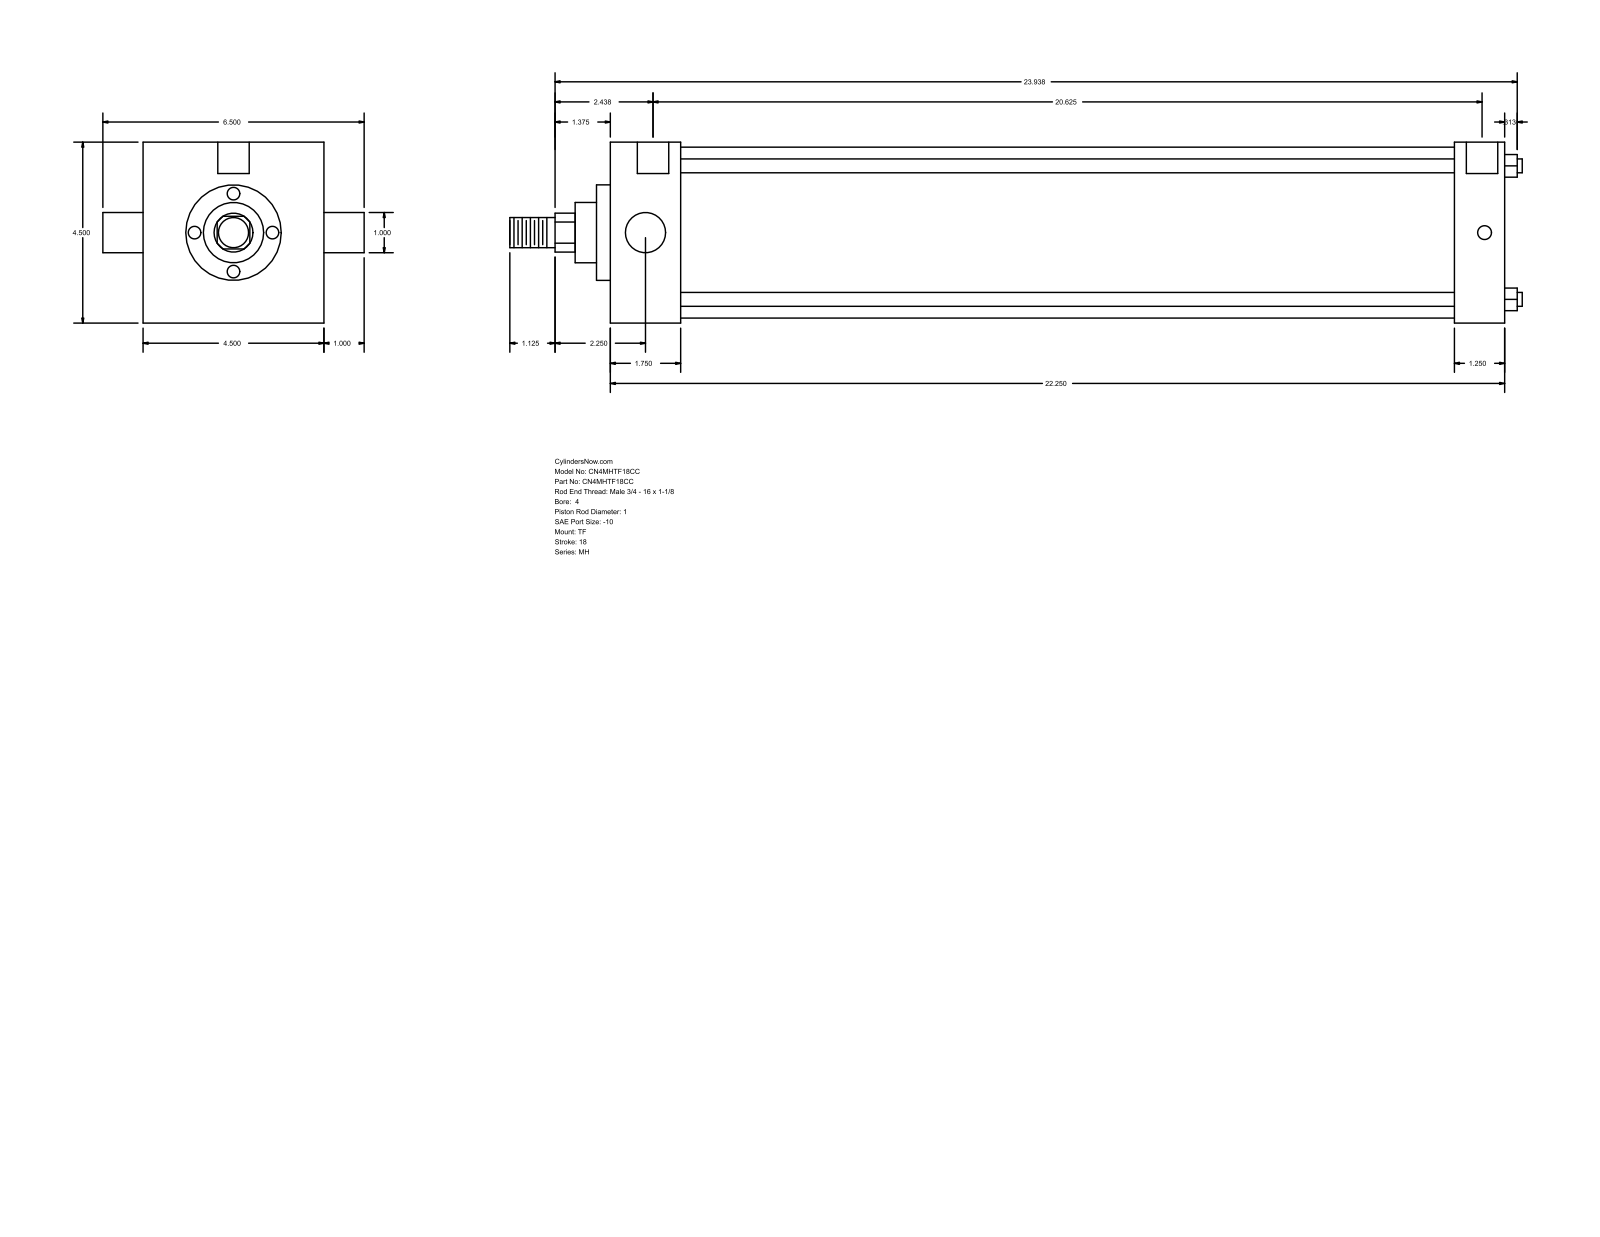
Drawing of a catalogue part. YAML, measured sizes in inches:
part_name: "MH_TF__0400_1"
step_written_by: "GSSL Pune (CONFIG_CONTROL_DESIGN)"
units: inches
bodies: {solids: 0, faces: 86, planar: 61, cylindrical: 25, other: 0}
overall_size: [25.187, 6.5, 4.5]
round_holes:
  - {diameter: 0.344, count: 3}
  - {diameter: 0.781, count: 2}
round_bosses_or_shafts:
  - {diameter: 0.345, count: 4}
  - {diameter: 1, count: 2}
  - {diameter: 4.25, count: 1}
  - {diameter: 2.375, count: 1}
  - {diameter: 1.5, count: 1}
  - {diameter: 0.75, count: 1}
partial_cylinders:
  - {radius: 0.484, count: 1}
face_to_face_distances: [4.5, 22.25, 1.75, 20.5, 21, 19.25, 1.25, 0.344, 2.094, 21.344]
hole_center_spacings: [0.062, 0.063, 20.625, 20.687, 20.688, 20.75]
